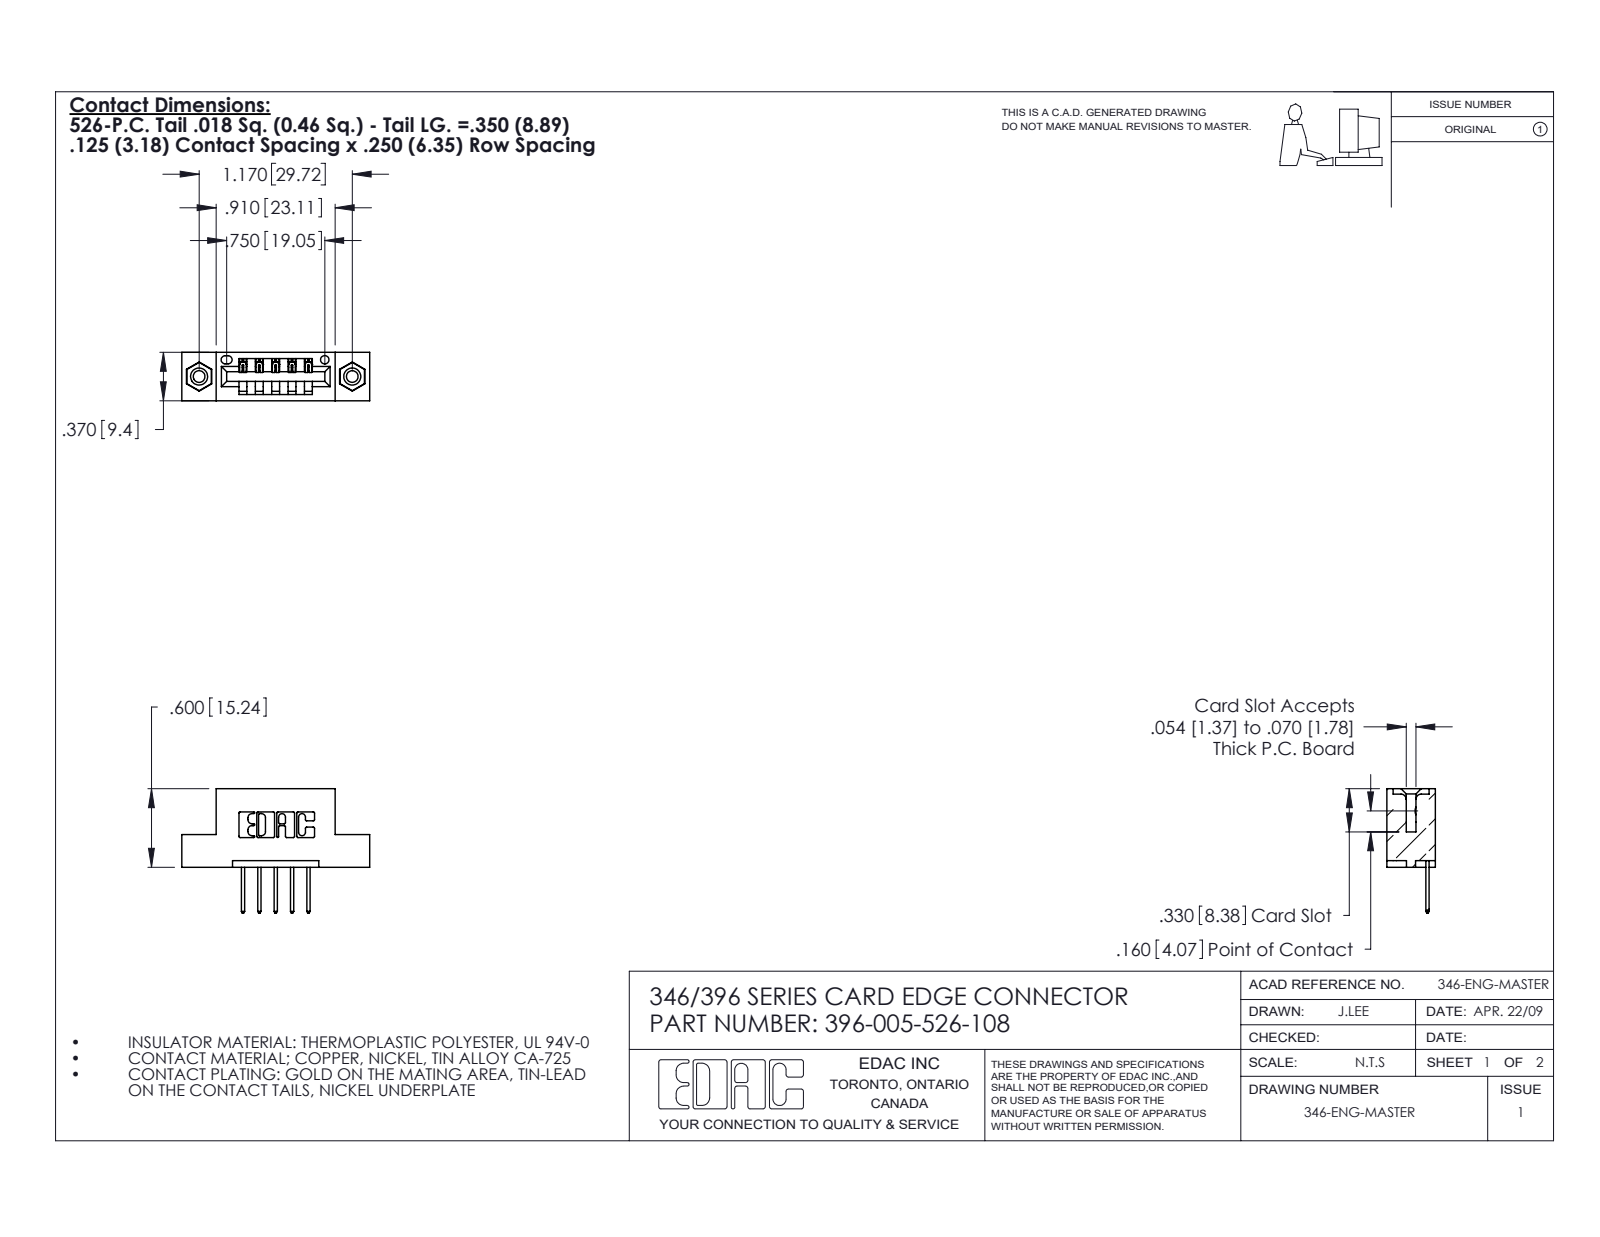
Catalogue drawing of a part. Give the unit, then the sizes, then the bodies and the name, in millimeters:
Units: millimetres
Overall size (bounding box): 36.4 × 24.1 × 9.4
Round holes (diameter × count): ⌀2.3 ×2, ⌀3.2 ×2, ⌀4 ×2, ⌀1.6 ×1
Round bosses / shafts (diameter × count): ⌀3.9 ×2
Partial cylindrical surfaces — rounded edges, fillets, slot ends (radius × count): R0.3 ×22, R0.2 ×10, R0.3 ×10, R0.2 ×6, R0.8 ×6, R0.7 ×3, R0.8 ×2, R1 ×2
Main face-to-face distances: 6.4, 9.4, 1.2, 8.2, 14, 3.8, 5.6, 2.5, 4.4, 3.2
Hole centre spacings: 6.2, 24.6, 29.7
Volume: 3 230 mm³ · Surface area: 3 646 mm²
Bodies: 8 solids, 472 faces (308 planar, 148 cylindrical, 16 other)
Part name (STEP PRODUCT): 396-005-526-108; 345-250-001_345-250-003-102; 346 Part_Flush Mounting Lugs - 0.156 Dia-TI; 345-292-001_345-293-126
STEP written by: SolidWorks 2020 (CONFIG_CONTROL_DESIGN)
